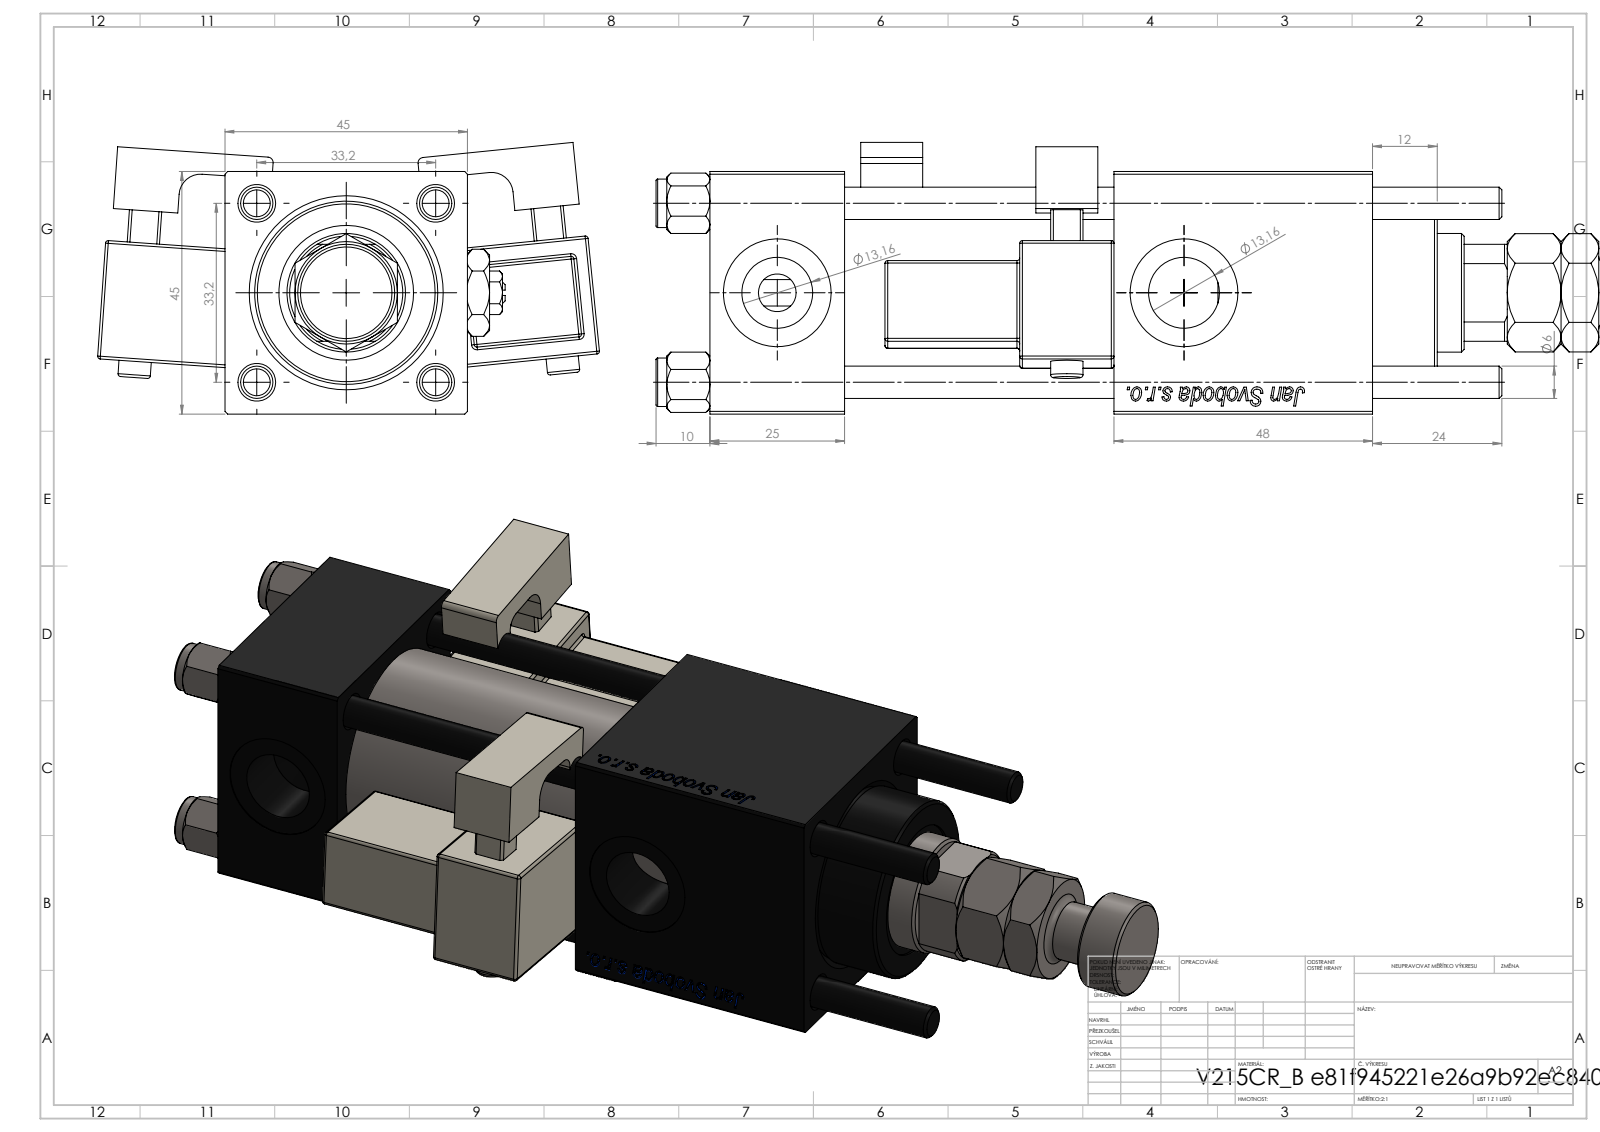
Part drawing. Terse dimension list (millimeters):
name: V215CR_VCP_B; NUT_M5_B; V215CR_B_TYCINKA; V215CR_B-1 (+4 more)
written by: SolidWorks 2019 (CONFIG_CONTROL_DESIGN)
unit: mm
bodies: 16 solids, 1466 faces (556 planar, 152 cylindrical, 758 other)
size: 191 × 93.14 × 50.4
volume: 261 506 mm³; area: 93 327 mm²
holes: 4× ⌀6, 2× ⌀7, 2× ⌀13.16, 2× ⌀20, 1× ⌀10.5, 1× ⌀22, 1× ⌀24, 1× ⌀25, 1× ⌀32, 1× ⌀33
bosses: 4× ⌀9, 2× ⌀6, 1× ⌀38, 1× ⌀34, 1× ⌀18, 1× ⌀11
rounds: 48× R0.5, 2× R1, 2× R2.5, 2× R4, 1× R10.5
face distances: 45, 25, 50, 75, 123, 3, 20, 15, 32.5, 17.5
hole spacings: 23.48, 33.2, 46.95, 75.5
